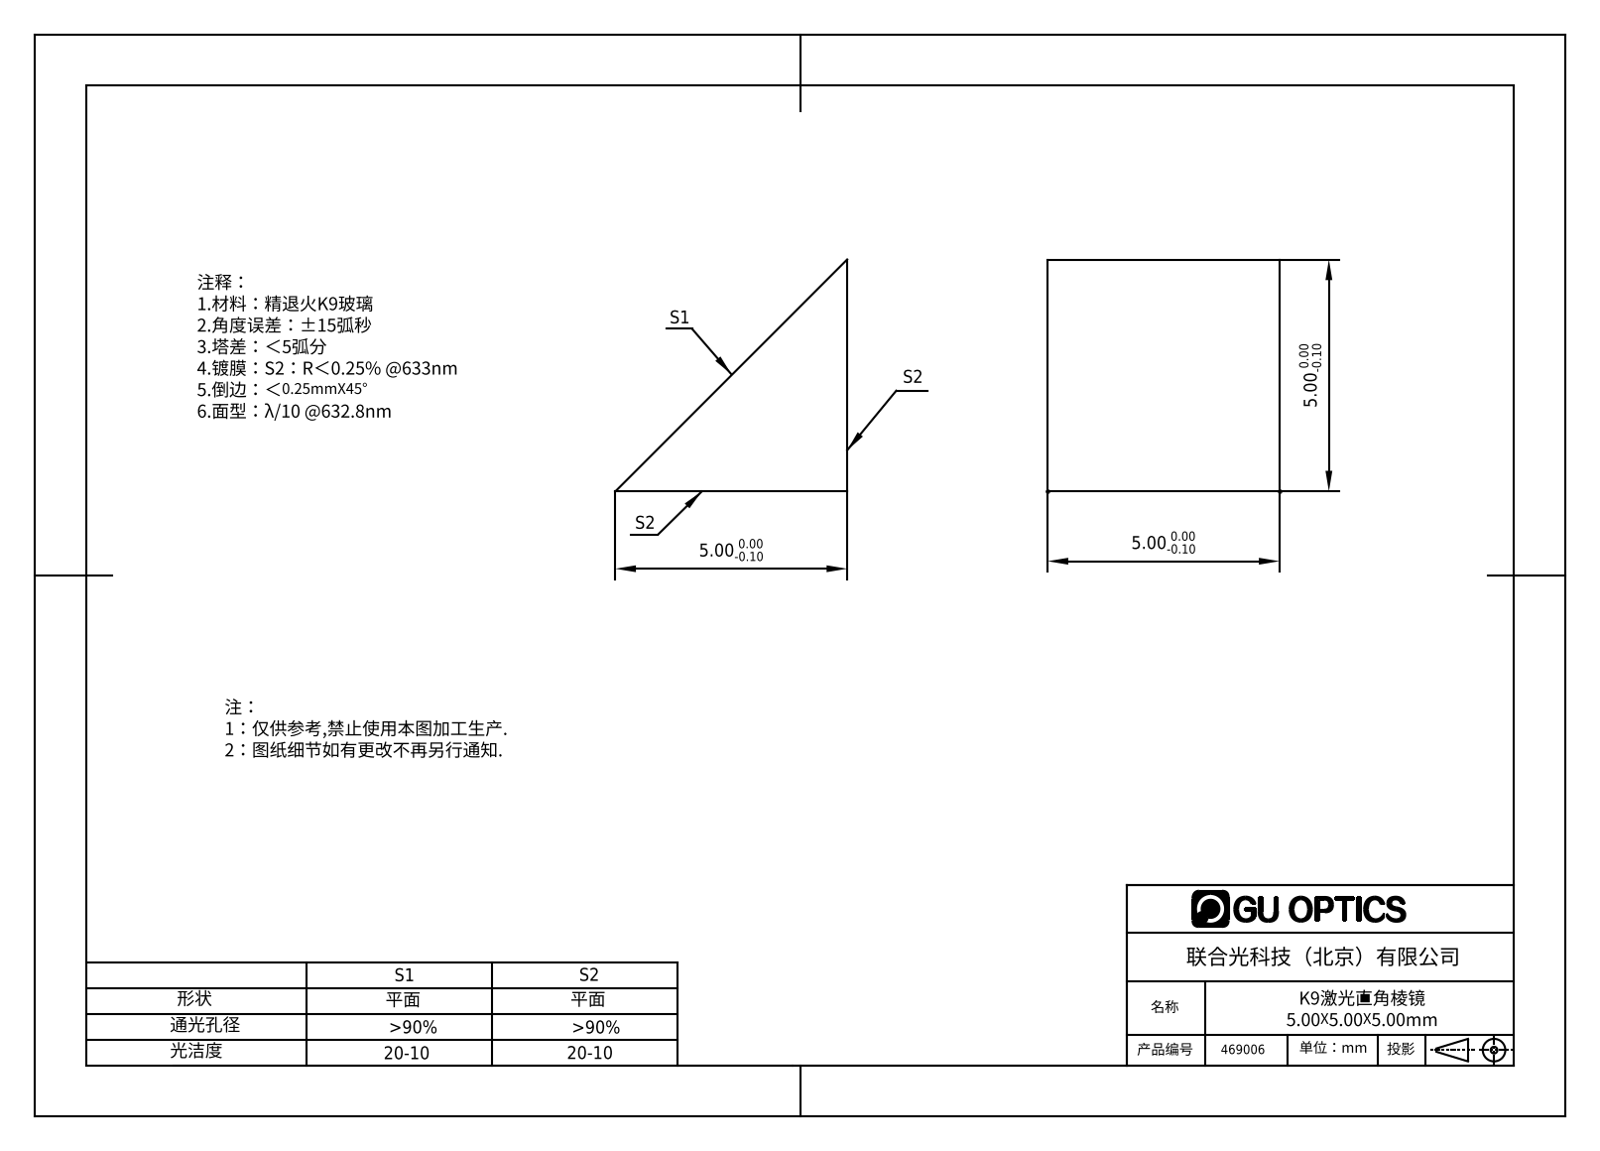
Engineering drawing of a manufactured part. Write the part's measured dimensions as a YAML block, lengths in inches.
part_name: "469000"
step_written_by: "SolidWorks 2016 (AUTOMOTIVE_DESIGN)"
units: inches
bodies: {solids: 1, faces: 5, planar: 5, cylindrical: 0, other: 0}
overall_size: [0.247, 0.197, 0.164]
volume: 0.004
surface_area: 0.164
face_to_face_distances: [0.197]
